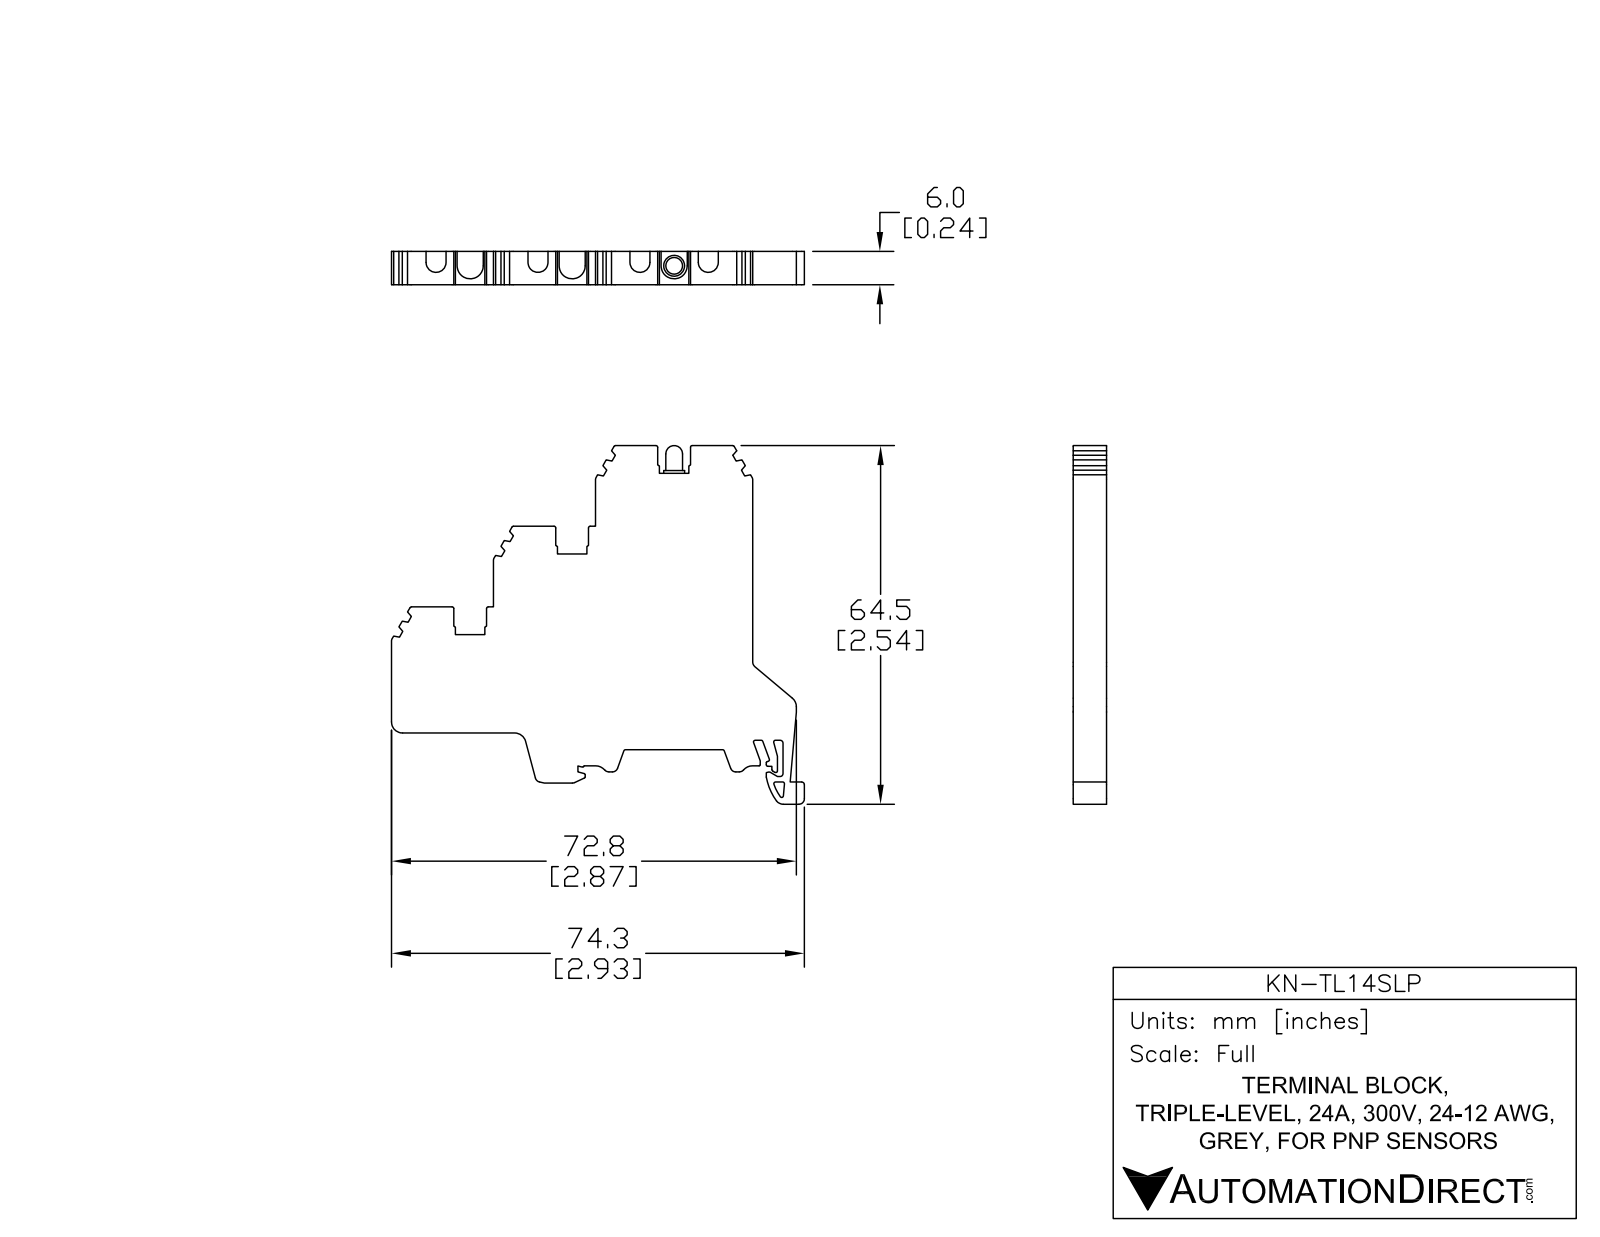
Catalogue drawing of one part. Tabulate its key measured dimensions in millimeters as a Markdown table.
| quantity | value |
| --- | --- |
| part name | KN-TL14SLP |
| STEP written by | SolidWorks 2014 (AUTOMOTIVE_DESIGN) |
| units | millimeters |
| bodies | 3 solids, 228 faces (151 planar, 76 cylindrical, 1 other) |
| overall size | 74.3 × 64.51 × 6 |
| volume | 16 307 mm³ |
| surface area | 7 900 mm² |
| round bosses / shafts (diameter × count) | 3.75 × 1, 3 × 1, 2.5 × 1 |
| partial cylindrical surfaces (radius × count) | 0.3 × 23, 1 × 8, 0.5 × 7, 0.2 × 6, 1.8 × 4, 2 × 4, 2.35 × 3, 2.13 × 2 |
| main face-to-face distances | 6, 14.5, 18.35, 1, 3, 4, 5, 54.7, 29, 9.5 |
